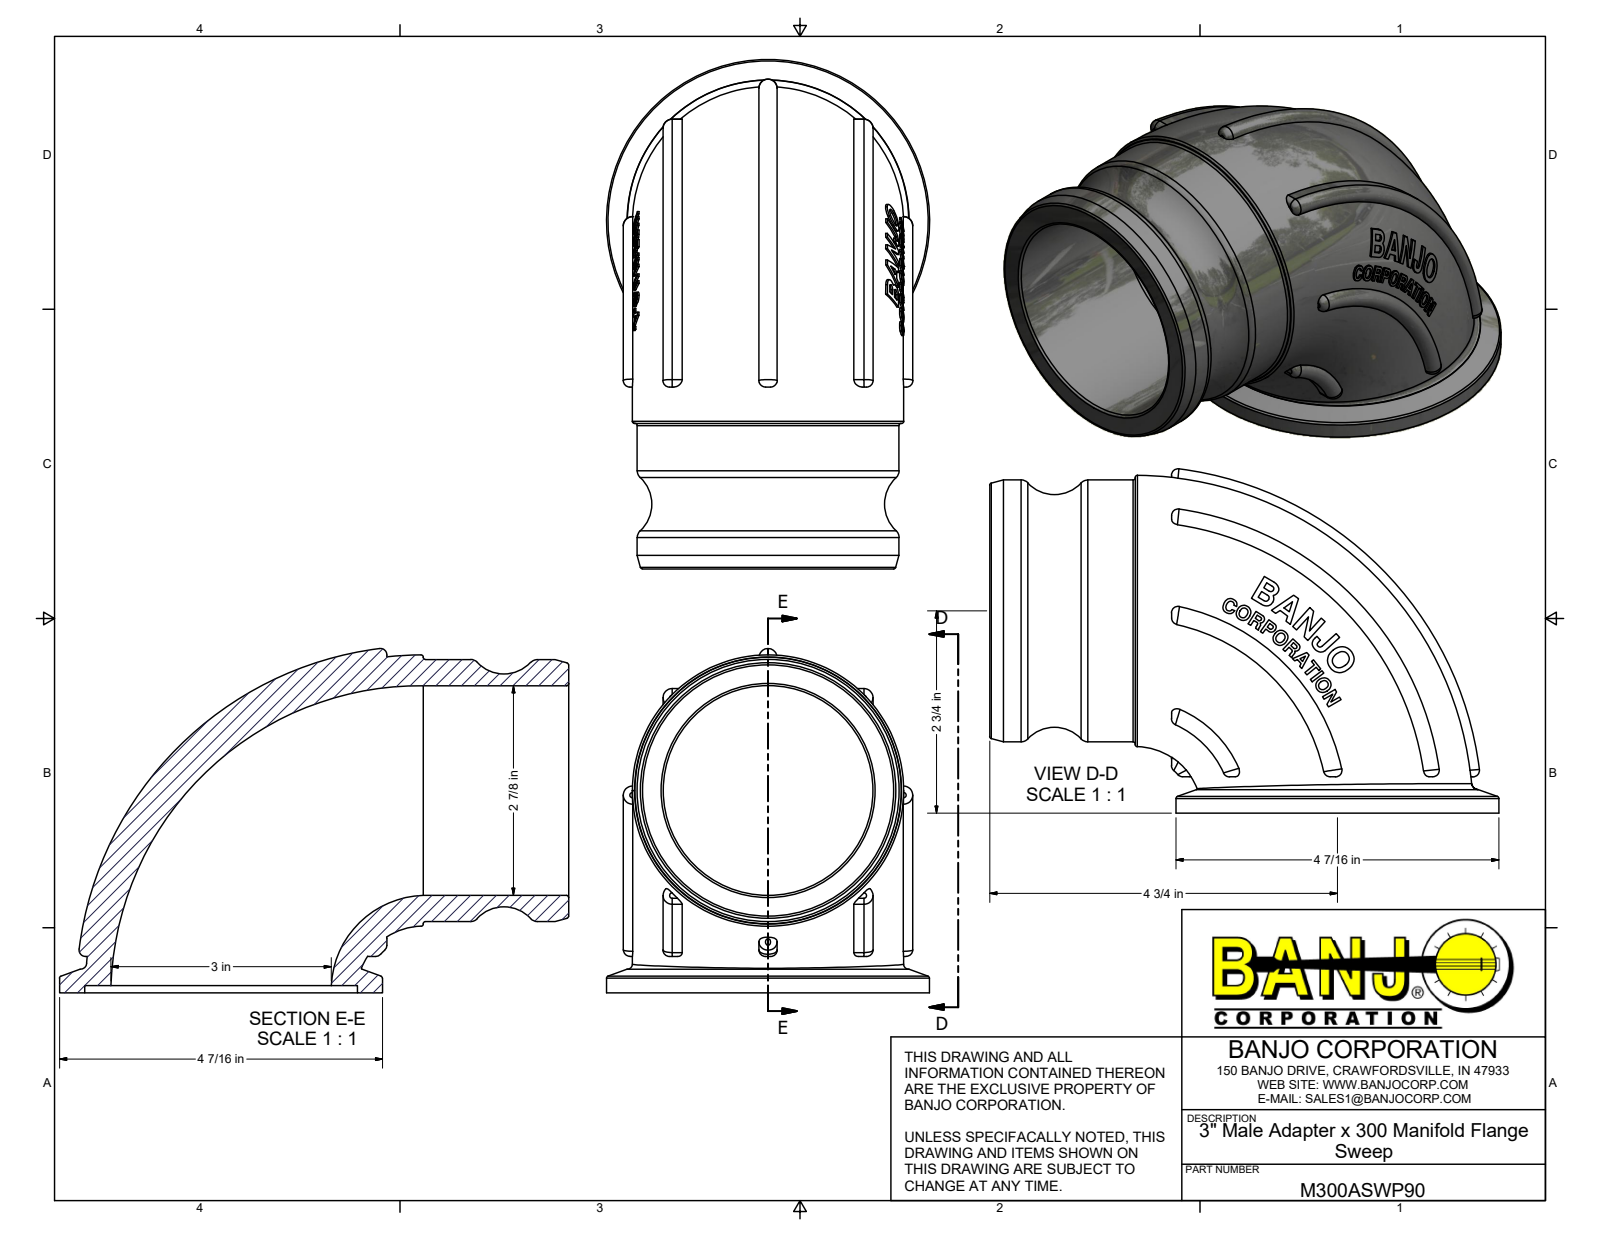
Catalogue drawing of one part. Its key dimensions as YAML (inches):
part_name: "M300ASWP90"
step_written_by: "Autodesk Inventor 2017 (AUTOMOTIVE_DESIGN)"
units: inches
bodies: {solids: 1, faces: 427, planar: 213, cylindrical: 17, other: 197}
overall_size: [7, 4.733, 4.44]
volume: 25.39
surface_area: 153
round_holes:
  - {diameter: 2.88, count: 1}
  - {diameter: 3.75, count: 1}
round_bosses_or_shafts:
  - {diameter: 4.44, count: 1}
  - {diameter: 3.6, count: 1}
partial_cylinders:
  - {radius: 0.09, count: 4}
  - {radius: 1.336, count: 1}
  - {radius: 4.224, count: 1}
face_to_face_distances: [0.1, 0.324, 0.224, 2, 0.5, 0.041, 0.4, 0.176, 2.5, 0.2]
